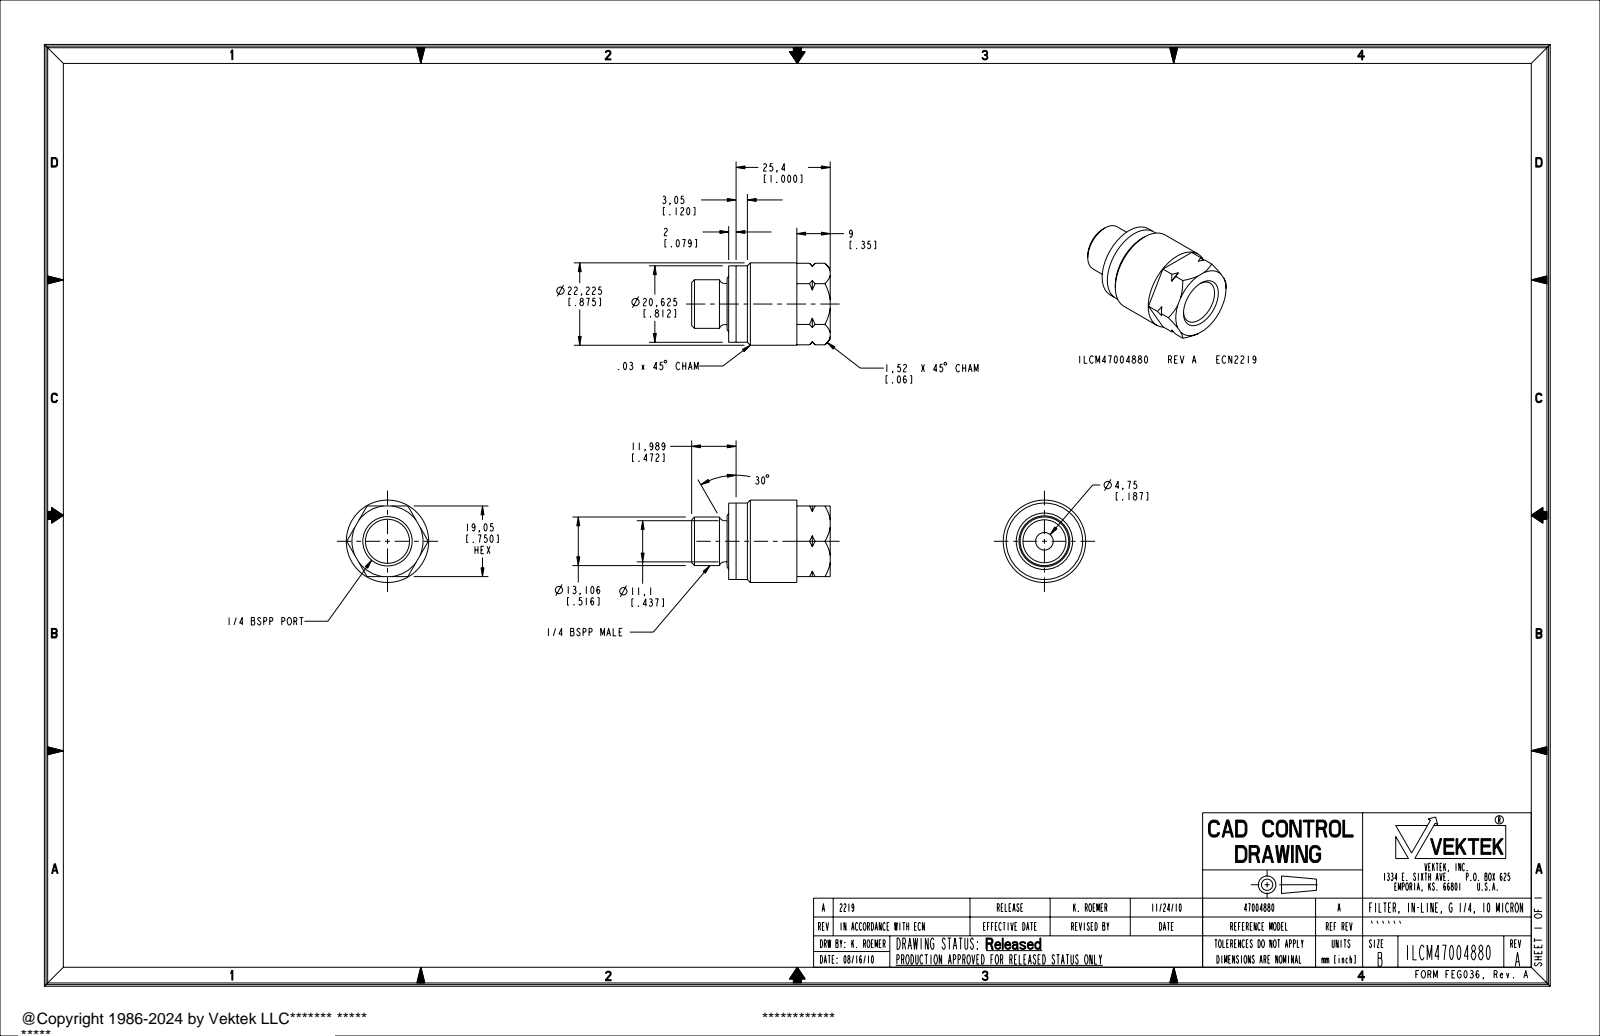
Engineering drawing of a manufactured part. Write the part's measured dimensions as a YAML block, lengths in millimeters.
part_name: "ILCM47004880"
step_written_by: "PRO/ENGINEER BY PARAMETRIC TECHNOLOGY CORPORATION, 2007460 (AUTOMOTIVE_DESIGN_CC2)"
units: millimeters
bodies: {solids: 1, faces: 64, planar: 14, cylindrical: 16, other: 34}
overall_size: [37.39, 22.23, 22.23]
volume: 9062
surface_area: 3887
round_holes:
  - {diameter: 4.75, count: 1}
  - {diameter: 11.89, count: 1}
  - {diameter: 13.74, count: 1}
round_bosses_or_shafts:
  - {diameter: 22.23, count: 1}
  - {diameter: 20.62, count: 1}
  - {diameter: 20.6, count: 1}
  - {diameter: 13.11, count: 1}
  - {diameter: 11.1, count: 1}
face_to_face_distances: [19.04, 27.4, 13.91, 13.49, 19.06, 9.99, 23.9, 37.39, 28.39, 18.4]
